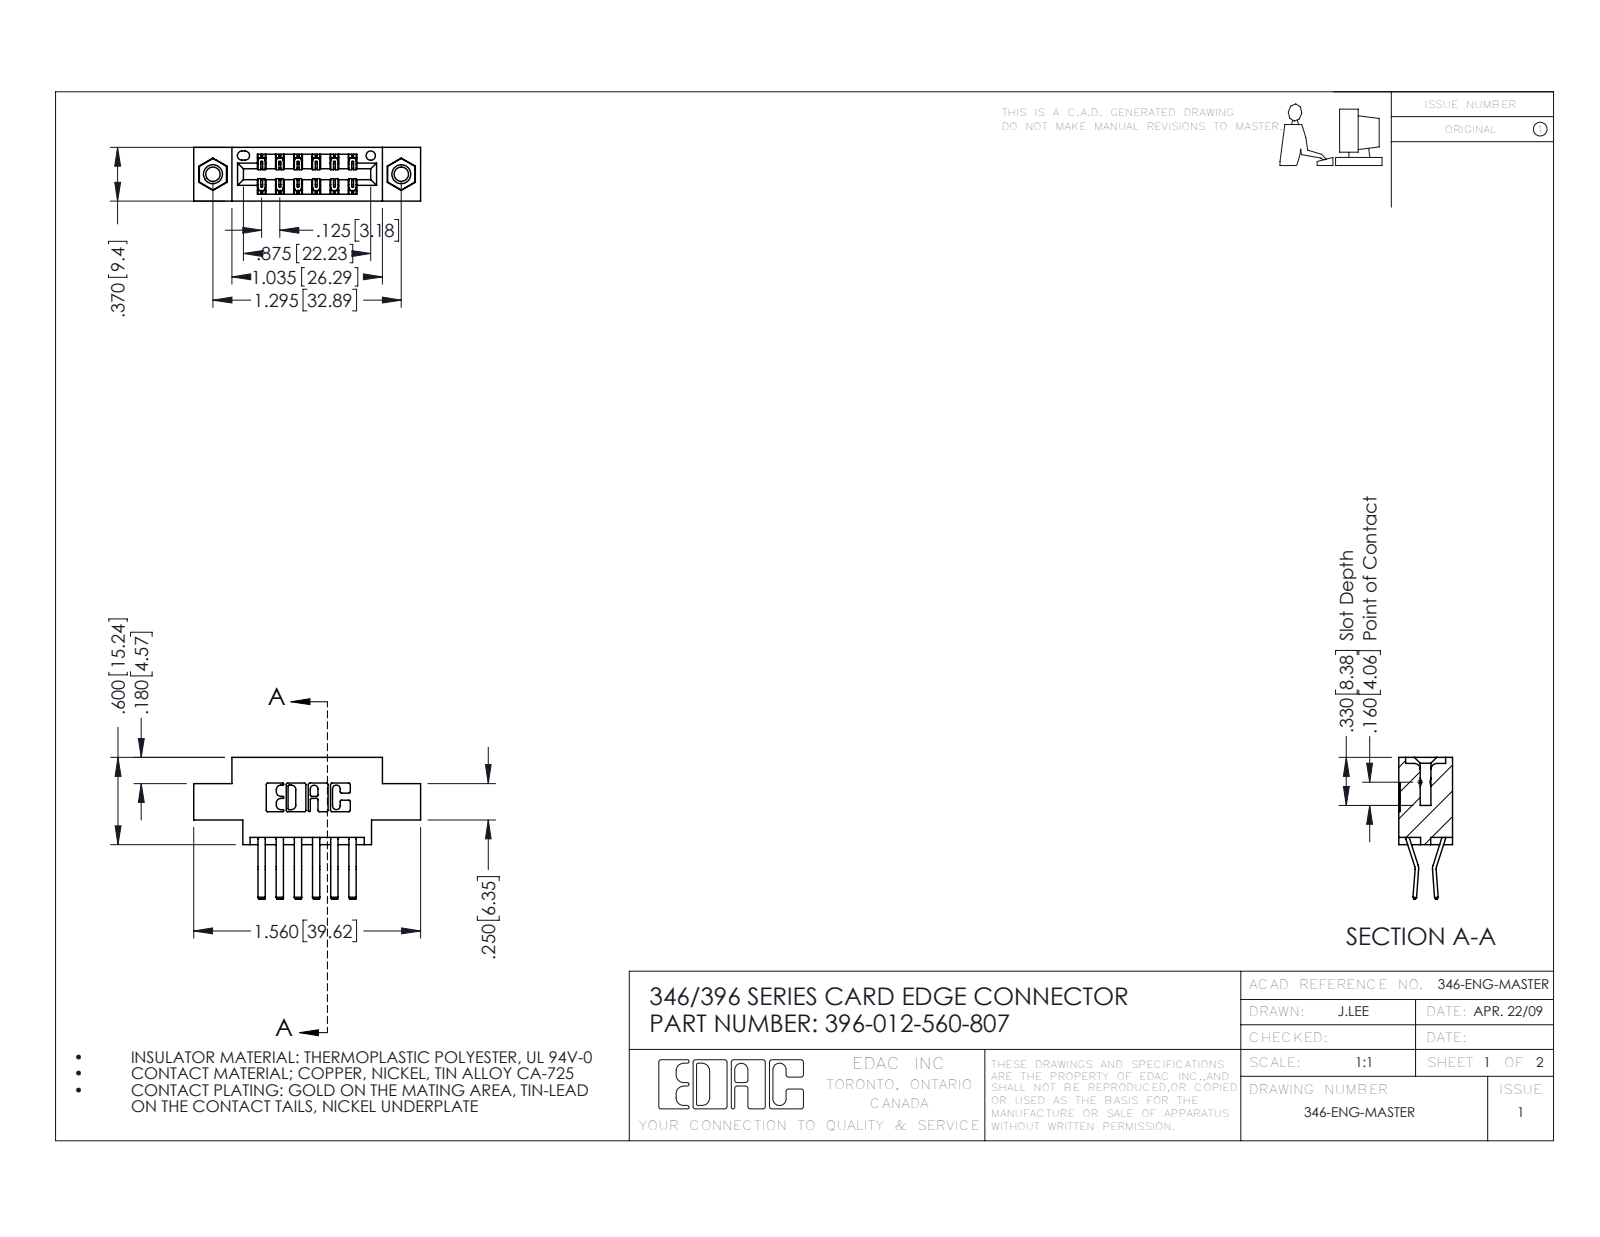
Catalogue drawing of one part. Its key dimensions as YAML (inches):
part_name: "345-250-001_345-250-005-103; 346 Part_0.170 Offset - 0.156 Dia-TI; 345-292-001_560 Tail; 396-012-560-807"
step_written_by: "SolidWorks 2016 (CONFIG_CONTROL_DESIGN)"
units: inches
bodies: {solids: 15, faces: 834, planar: 532, cylindrical: 286, other: 16}
overall_size: [1.56, 0.975, 0.37]
volume: 0.213
surface_area: 7.225
round_holes:
  - {diameter: 0.098, count: 2}
  - {diameter: 0.125, count: 2}
  - {diameter: 0.156, count: 2}
  - {diameter: 0.064, count: 1}
round_bosses_or_shafts:
  - {diameter: 0.155, count: 2}
partial_cylinders:
  - {radius: 0.01, count: 22}
  - {radius: 0.006, count: 18}
  - {radius: 0.007, count: 6}
  - {radius: 0.031, count: 6}
  - {radius: 0.026, count: 3}
  - {radius: 0.01, count: 2}
  - {radius: 0.014, count: 2}
  - {radius: 0.022, count: 2}
face_to_face_distances: [0.25, 0.37, 0.048, 0.322, 0.025, 0.222, 0.148, 0.1, 0.174, 0.072]
hole_center_spacings: [0.246, 1.092, 1.295]
